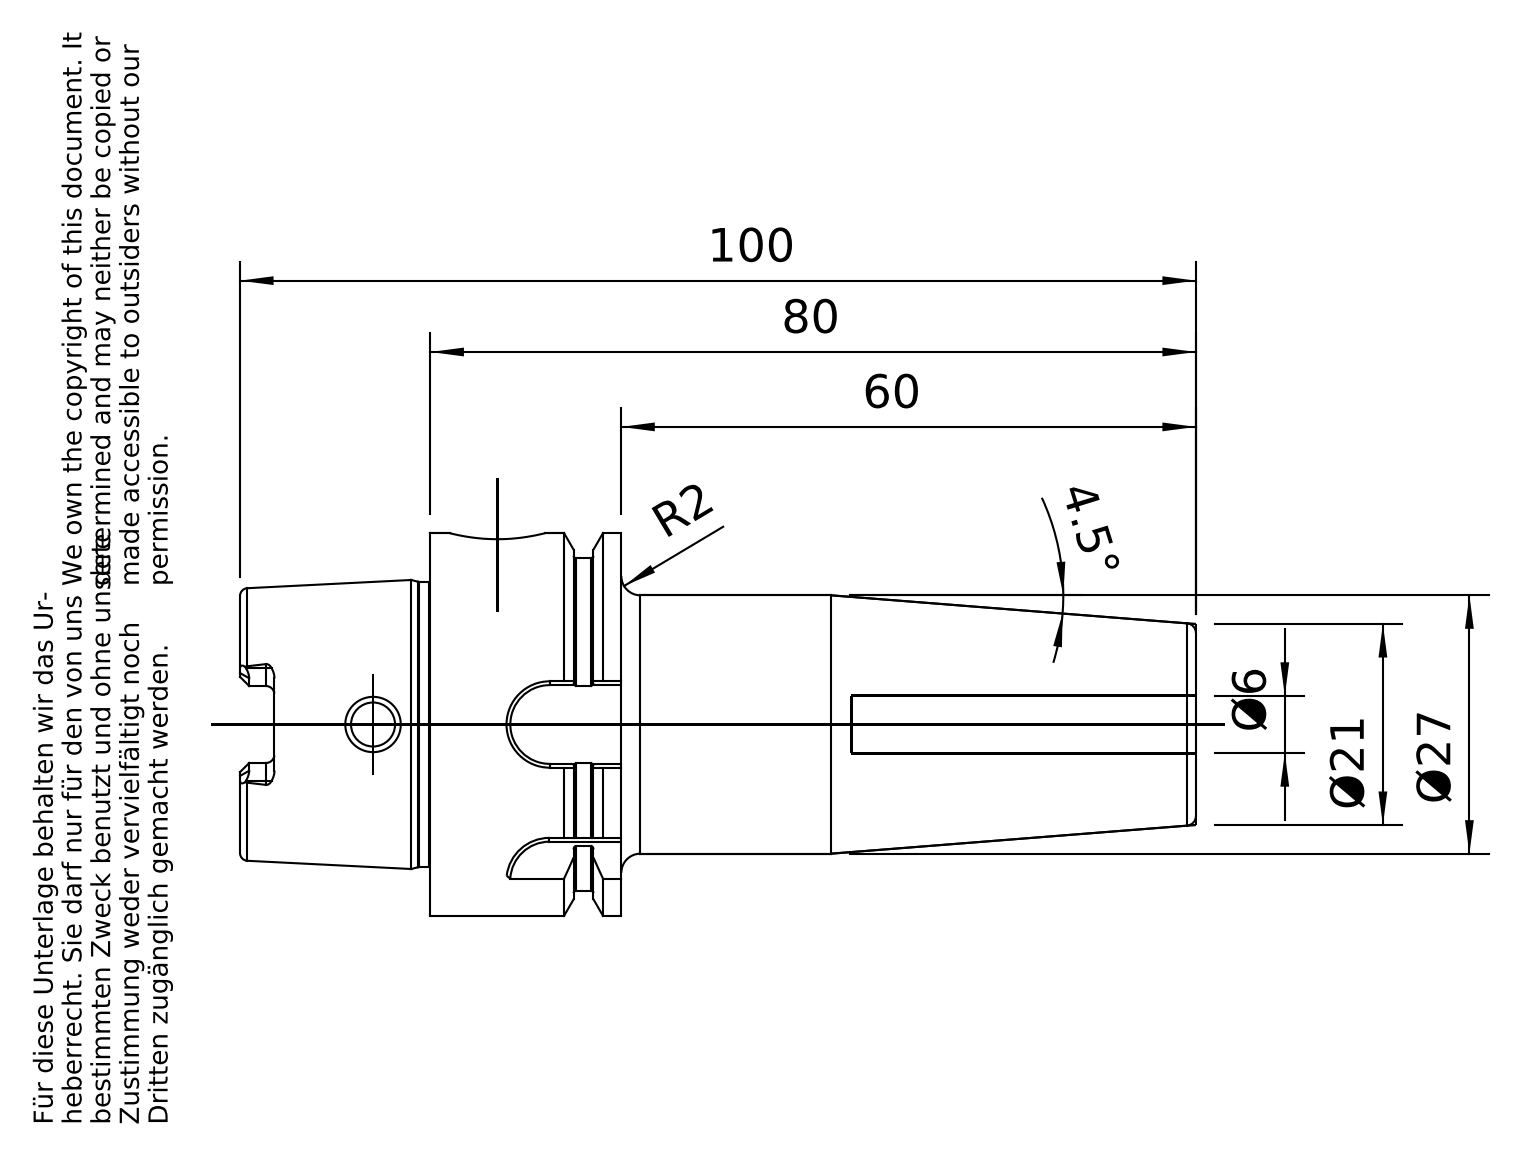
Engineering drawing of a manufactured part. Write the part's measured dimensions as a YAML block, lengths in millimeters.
part_name: "A40-140-06"
step_written_by: "PRO/ENGINEER BY PARAMETRIC TECHNOLOGY CORPORATION, 2010430 (CONFIG_CONTROL_DESIGN)"
units: millimeters
bodies: {solids: 1, faces: 184, planar: 60, cylindrical: 50, other: 74}
overall_size: [99.9, 40, 40]
volume: 53022
surface_area: 14839
round_holes:
  - {diameter: 4.6, count: 1}
  - {diameter: 6, count: 1}
  - {diameter: 10, count: 1}
  - {diameter: 10.2, count: 1}
  - {diameter: 12, count: 1}
  - {diameter: 12.22, count: 1}
  - {diameter: 12.5, count: 1}
  - {diameter: 21.04, count: 1}
  - {diameter: 25.57, count: 1}
round_bosses_or_shafts:
  - {diameter: 40, count: 1}
  - {diameter: 34.75, count: 1}
  - {diameter: 29.81, count: 1}
  - {diameter: 27, count: 1}
partial_cylinders:
  - {radius: 0.9, count: 6}
  - {radius: 1.88, count: 4}
  - {radius: 4.5, count: 3}
  - {radius: 4.51, count: 1}
face_to_face_distances: [19.95, 80, 60.05, 7.95, 12, 72.05, 19.9, 27.85, 39.85, 99.9]
